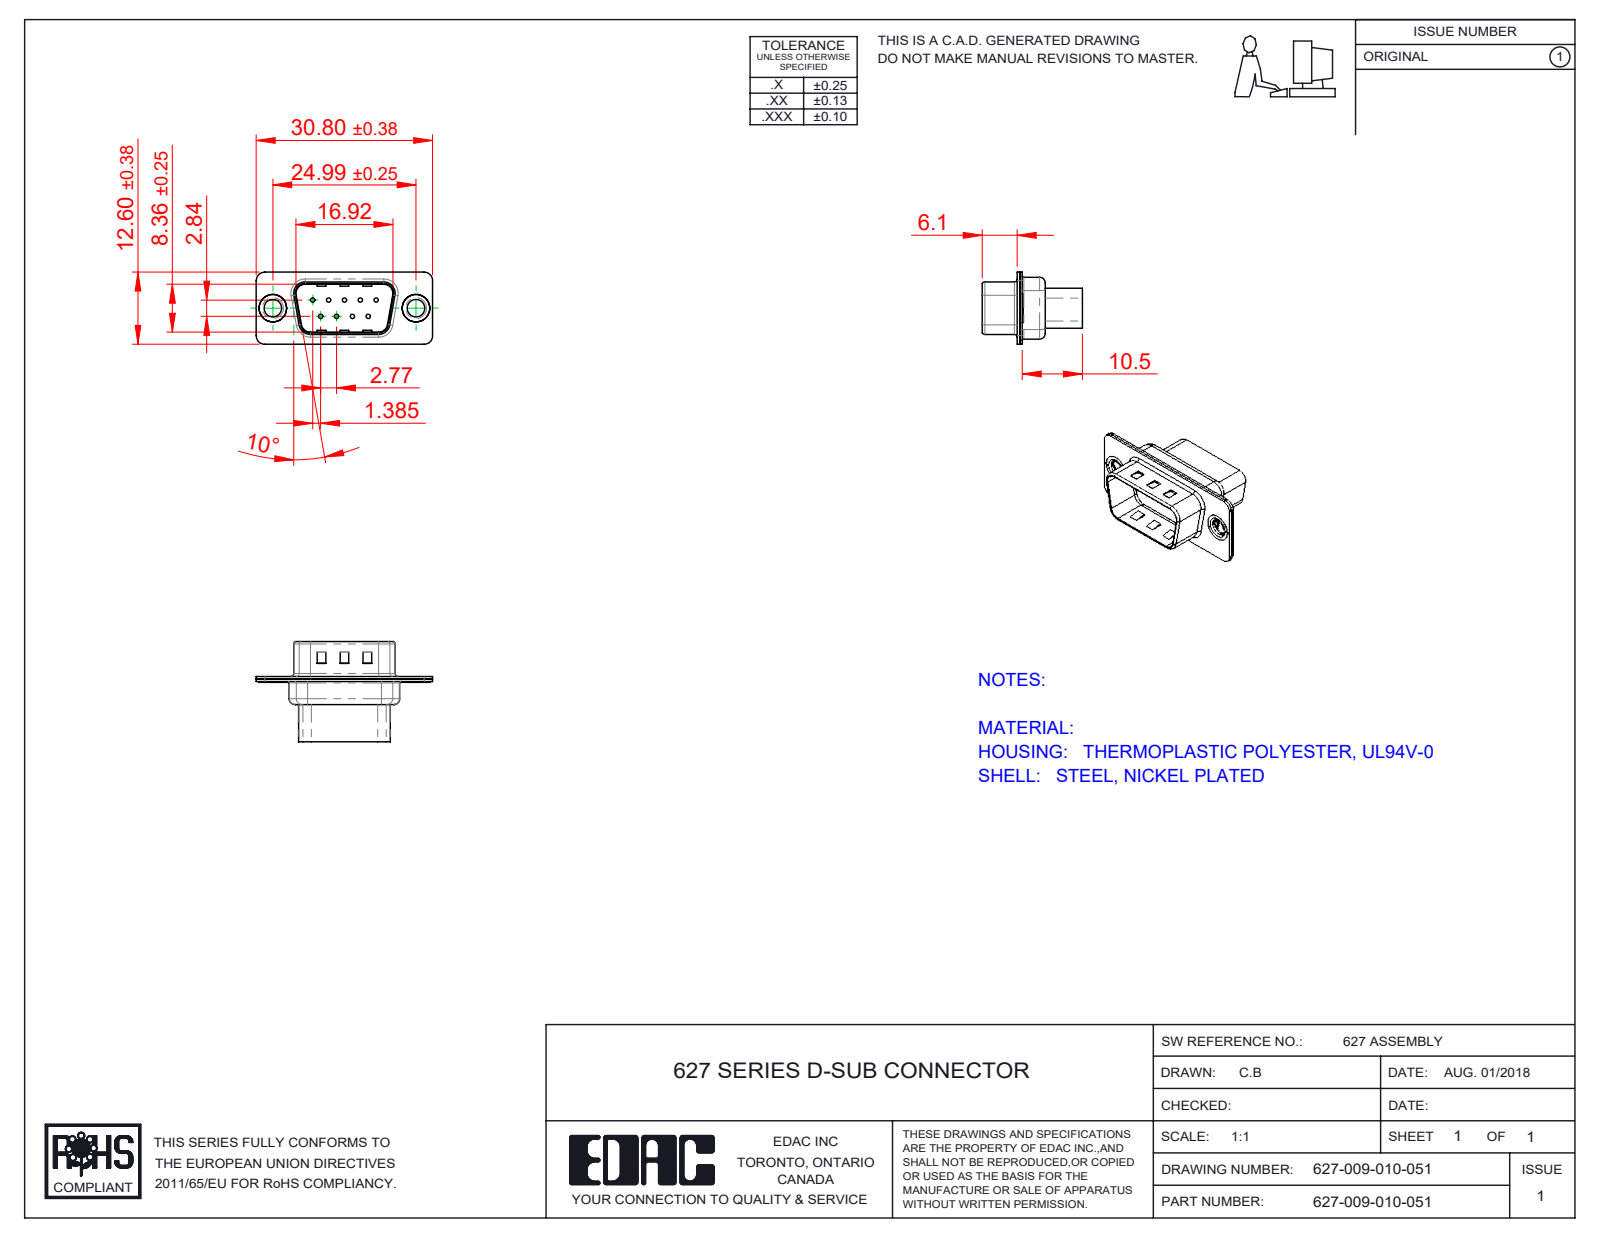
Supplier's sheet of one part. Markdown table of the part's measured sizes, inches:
| quantity | value |
| --- | --- |
| part name | 627 Shell Rear_09 Contacts; 627-009-010-251; 627 Shell Front_09 Contacts; 627 Housing_09 HP (+1 more) |
| STEP written by | SolidWorks 2020 (CONFIG_CONTROL_DESIGN) |
| units | inches |
| bodies | 5 solids, 350 faces (125 planar, 167 cylindrical, 58 other) |
| overall size | 1.213 × 0.689 × 0.496 |
| volume | 0.097 in³ |
| surface area | 5.31 in² |
| round holes (diameter × count) | 0.03 × 9, 0.063 × 9, 0.079 × 9, 0.12 × 2, 0.157 × 2, 0.189 × 2 |
| round bosses / shafts (diameter × count) | 0.197 × 2, 0.193 × 2, 0.14 × 2 |
| partial cylindrical surfaces (radius × count) | 0.059 × 18, 0.079 × 12, 0.02 × 8, 0.063 × 8, 0.01 × 4, 0.024 × 4, 0.026 × 4, 0.035 × 4 |
| main face-to-face distances | 0.018, 0.016, 0.035, 0.032, 0.377, 0.055, 0.027, 0.302, 0.043, 0.318 |
| hole center spacings | 0.124, 0.109, 0.218, 0.198, 0.198, 0.327, 0.294, 0.295 |
